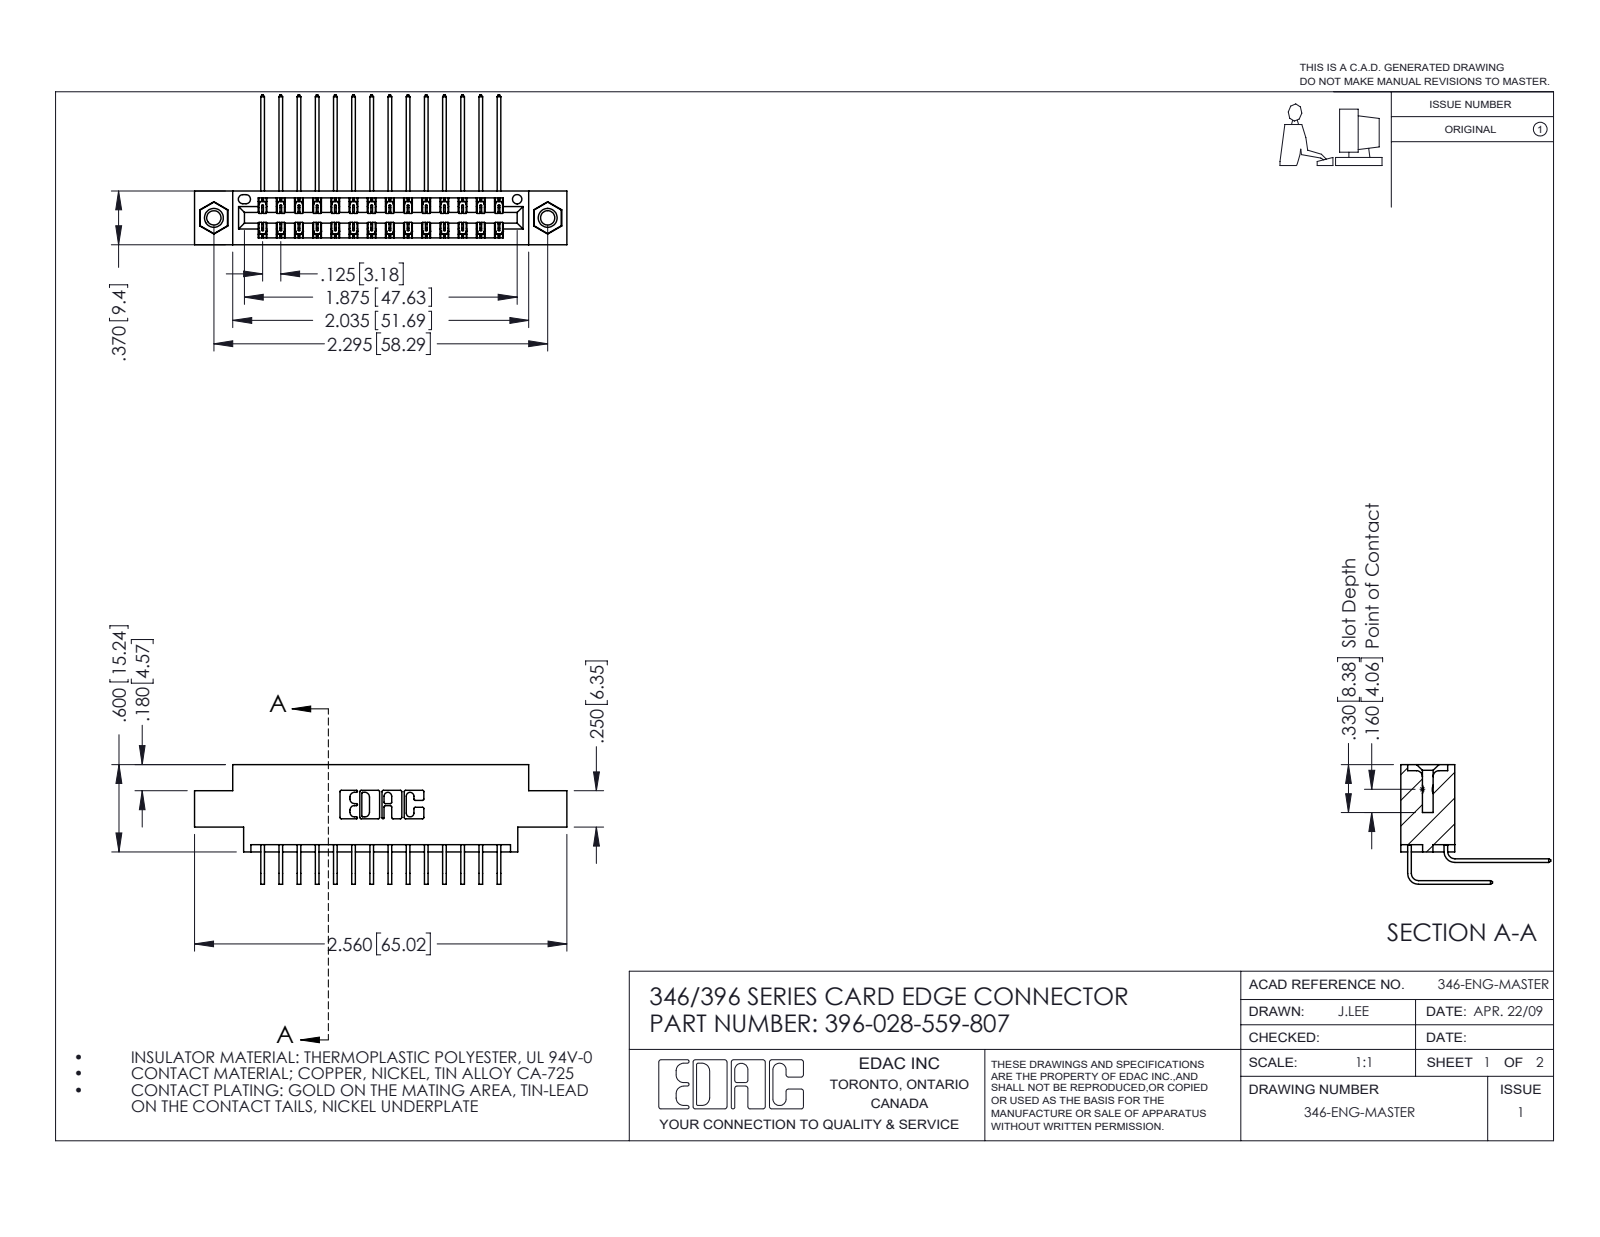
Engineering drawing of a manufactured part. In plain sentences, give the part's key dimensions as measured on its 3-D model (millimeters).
The part is named "346 Part_0.170 Offset - 0.156 Dia-TI; 345-250-001_345-250-005-103; 345-292-001_559 Tail - 2; 396-028-559-807 (+1 more)". Its 3-D file was written by "SolidWorks 2016 (CONFIG_CONTROL_DESIGN)". It is 31 solids with 1698 faces: 1148 planar, 534 cylindrical and 16 other. Overall it measures 65 by 26.2 by 20.9 millimeters. Its volume is 6 110 cubic millimeters and its surface area 8 955 square millimeters. Round holes: 2 of diameter 2.5, 2 of diameter 3.2, 2 of diameter 4, 1 of diameter 1.6. Round bosses or shafts: 2 of diameter 3.9. Partial cylindrical surfaces (rounded edges, fillets, slot ends): 42 of radius 0.2, 22 of radius 0.3, 6 of radius 0.2, 6 of radius 0.8, 3 of radius 0.7, 2 of radius 0.4, 2 of radius 0.6, 2 of radius 0.6. The main face-to-face distances are 1.2, 8.2, 9.4, 6.4, 0.6, 1.8, 7.6, 5.6, 7, 3.8. The hole center spacings are 6.2, 53.1, 58.3.
